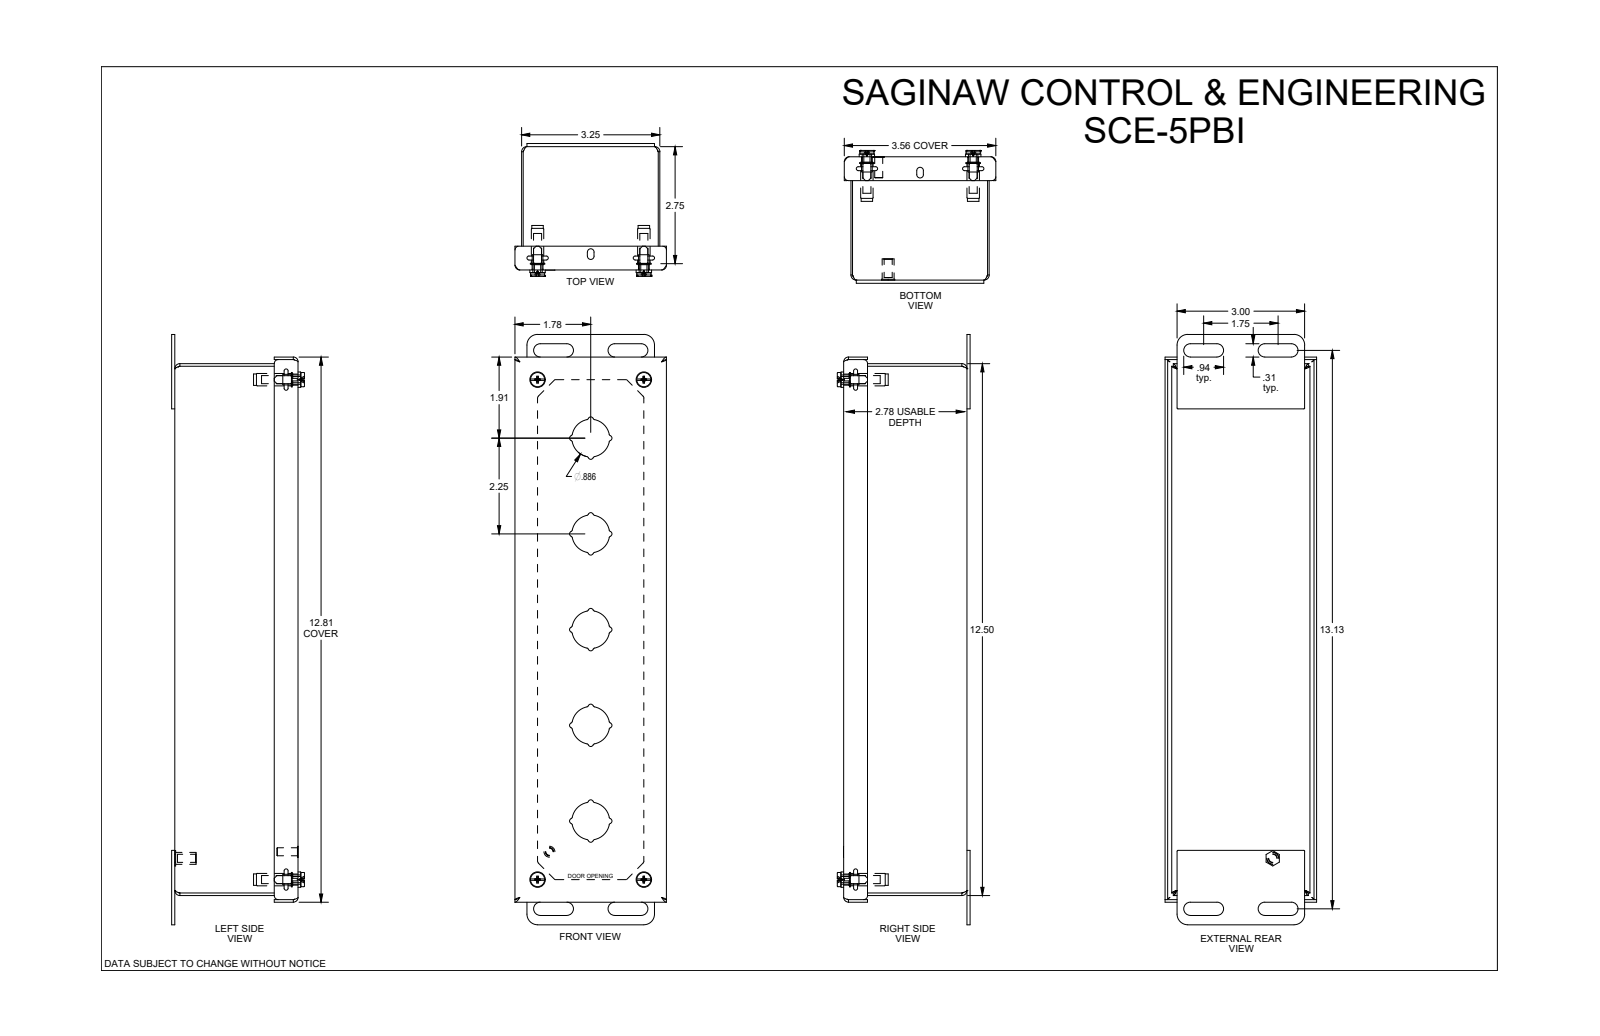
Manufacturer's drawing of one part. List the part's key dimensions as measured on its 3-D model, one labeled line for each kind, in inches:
Part name (STEP PRODUCT): SCE-5PBI
STEP written by: SolidWorks 2021 (AUTOMOTIVE_DESIGN)
Units: inches
Bodies: 3 solids, 496 faces (153 planar, 259 cylindrical, 84 other)
Overall size (bounding box): 13.875 × 3.563 × 3.036
Volume: 13.06 in³ · Surface area: 422.8 in²
Round holes (diameter × count): ⌀0.19 ×5, ⌀0.22 ×4, ⌀0.25 ×4, ⌀0.266 ×4, ⌀0.317 ×4
Round bosses / shafts (diameter × count): ⌀0.362 ×4, ⌀0.34 ×4, ⌀0.292 ×4, ⌀0.27 ×4, ⌀0.26 ×4, ⌀0.28 ×1, ⌀0.256 ×1, ⌀0.188 ×1
Partial cylindrical surfaces — rounded edges, fillets, slot ends (radius × count): R0.04 ×40, R0.06 ×20, R0.062 ×20, R0.015 ×8, R0.115 ×8, R0.156 ×8, R0.245 ×8, R0.443 ×5
Main face-to-face distances: 0.06, 2.838, 3.19, 2.778, 2.898, 3.25, 3.13, 0.156, 3.346, 2.69
Hole centre spacings: 2.5, 11.75, 11.75, 12.013, 12.013, 2.061, 2.5, 2.5
